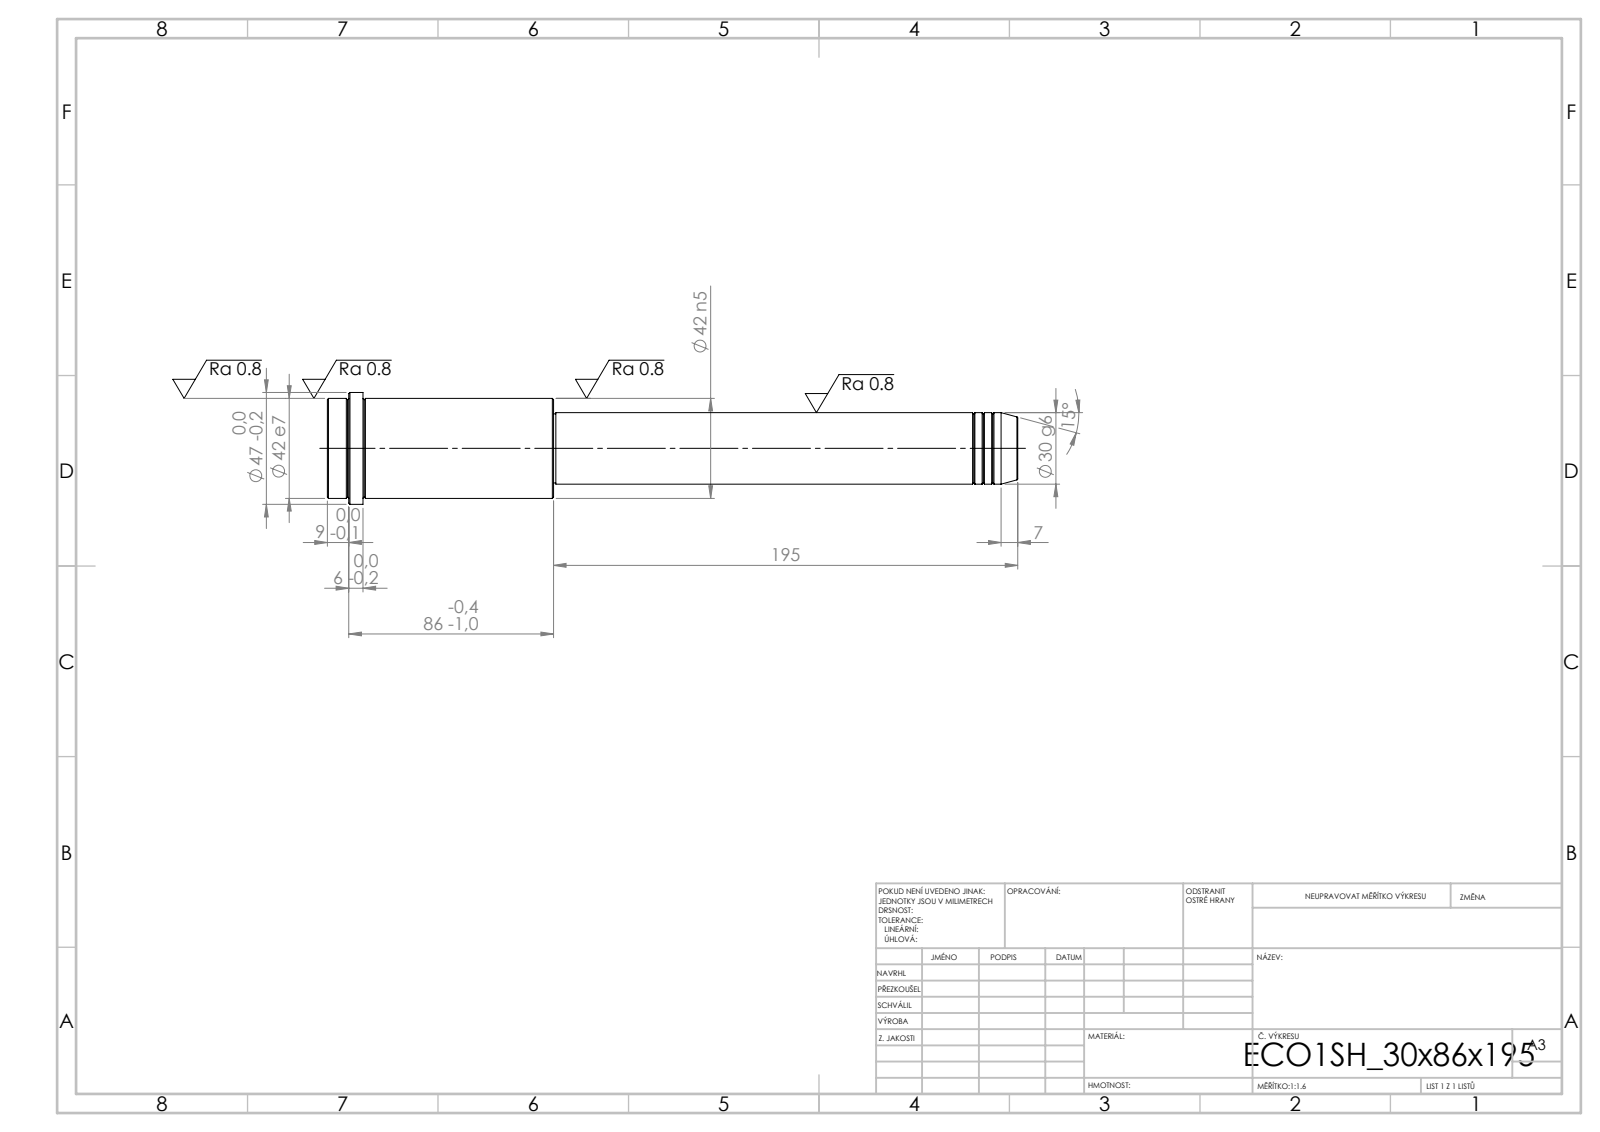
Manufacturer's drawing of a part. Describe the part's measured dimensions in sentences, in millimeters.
Its 3-D file was written by "SolidWorks 2019 (CONFIG_CONTROL_DESIGN)". It is 1 solid with 52 faces: 6 planar, 16 cylindrical and 30 other. Overall it measures 290 by 47 by 47 millimeters. Its volume is 270 647 cubic millimeters and its surface area 34 547 square millimeters. Round bosses or shafts: 1 of diameter 47, 1 of diameter 42, 1 of diameter 30, 1 of diameter 29. The main face-to-face distances are 95, 195, 290, 275, 80, 15, 281, 86, 6, 9.
